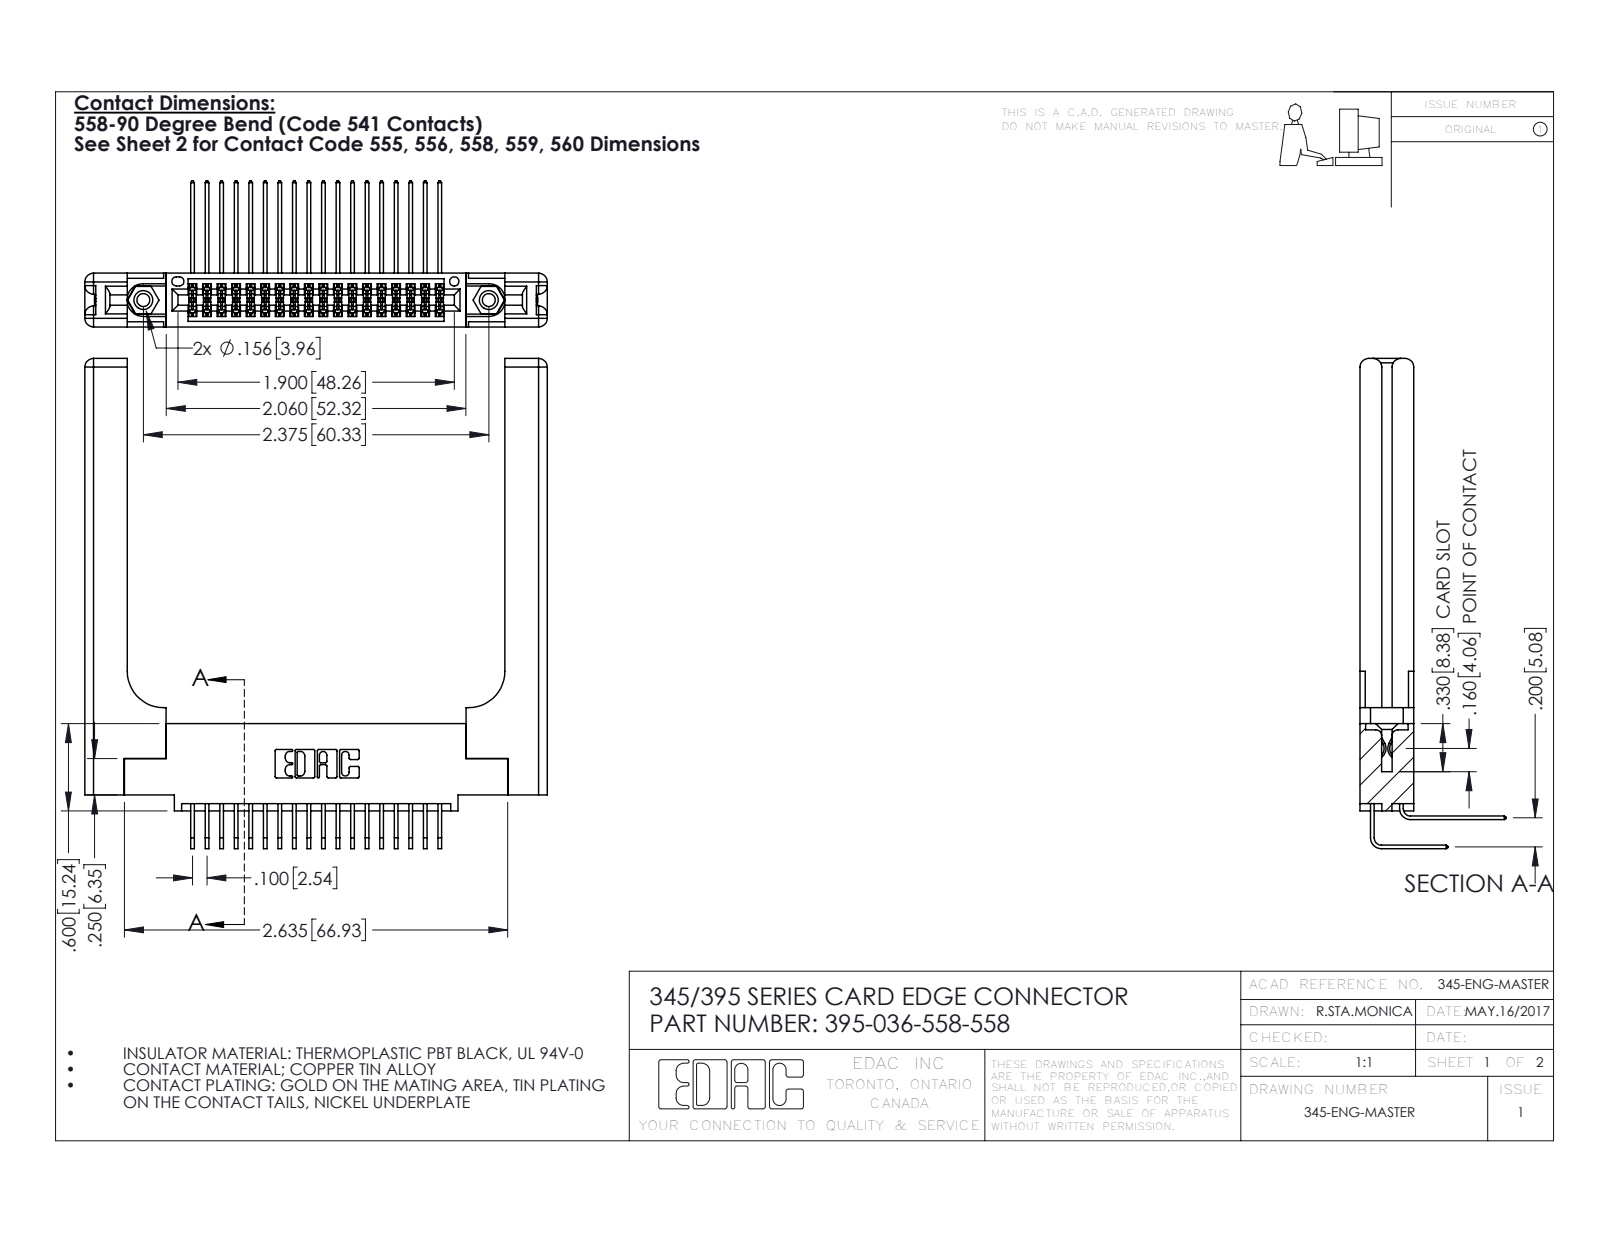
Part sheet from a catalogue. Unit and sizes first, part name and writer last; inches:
Units: inches
Overall size (bounding box): 3.369 × 3.179 × 1.005
Round holes (diameter × count): ⌀0.089 ×2, ⌀0.125 ×2, ⌀0.156 ×2, ⌀0.064 ×1
Round bosses / shafts (diameter × count): ⌀0.155 ×2
Partial cylindrical surfaces — rounded edges, fillets, slot ends (radius × count): R0.006 ×55, R0.01 ×22, R0.06 ×16, R0.007 ×6, R0.031 ×6, R0.026 ×3, R0.014 ×2, R0.019 ×2
Main face-to-face distances: 0.37, 0.072, 0.298, 0.2, 0.148, 0.15, 0.077, 0.22, 0.098, 0.272
Hole centre spacings: 0.27, 2.141, 2.375
Volume: 0.99 in³ · Surface area: 26.55 in²
Bodies: 41 solids, 2258 faces (1492 planar, 706 cylindrical, 60 other)
Part name (STEP PRODUCT): 345-292-001_558 Tail - 2; 395-036-558-558; 345-220-058_345-220-058; 345 Part_0.110 Offset - 0.156 Dia-TH (+2 more)
STEP written by: SolidWorks 2016 (CONFIG_CONTROL_DESIGN)
